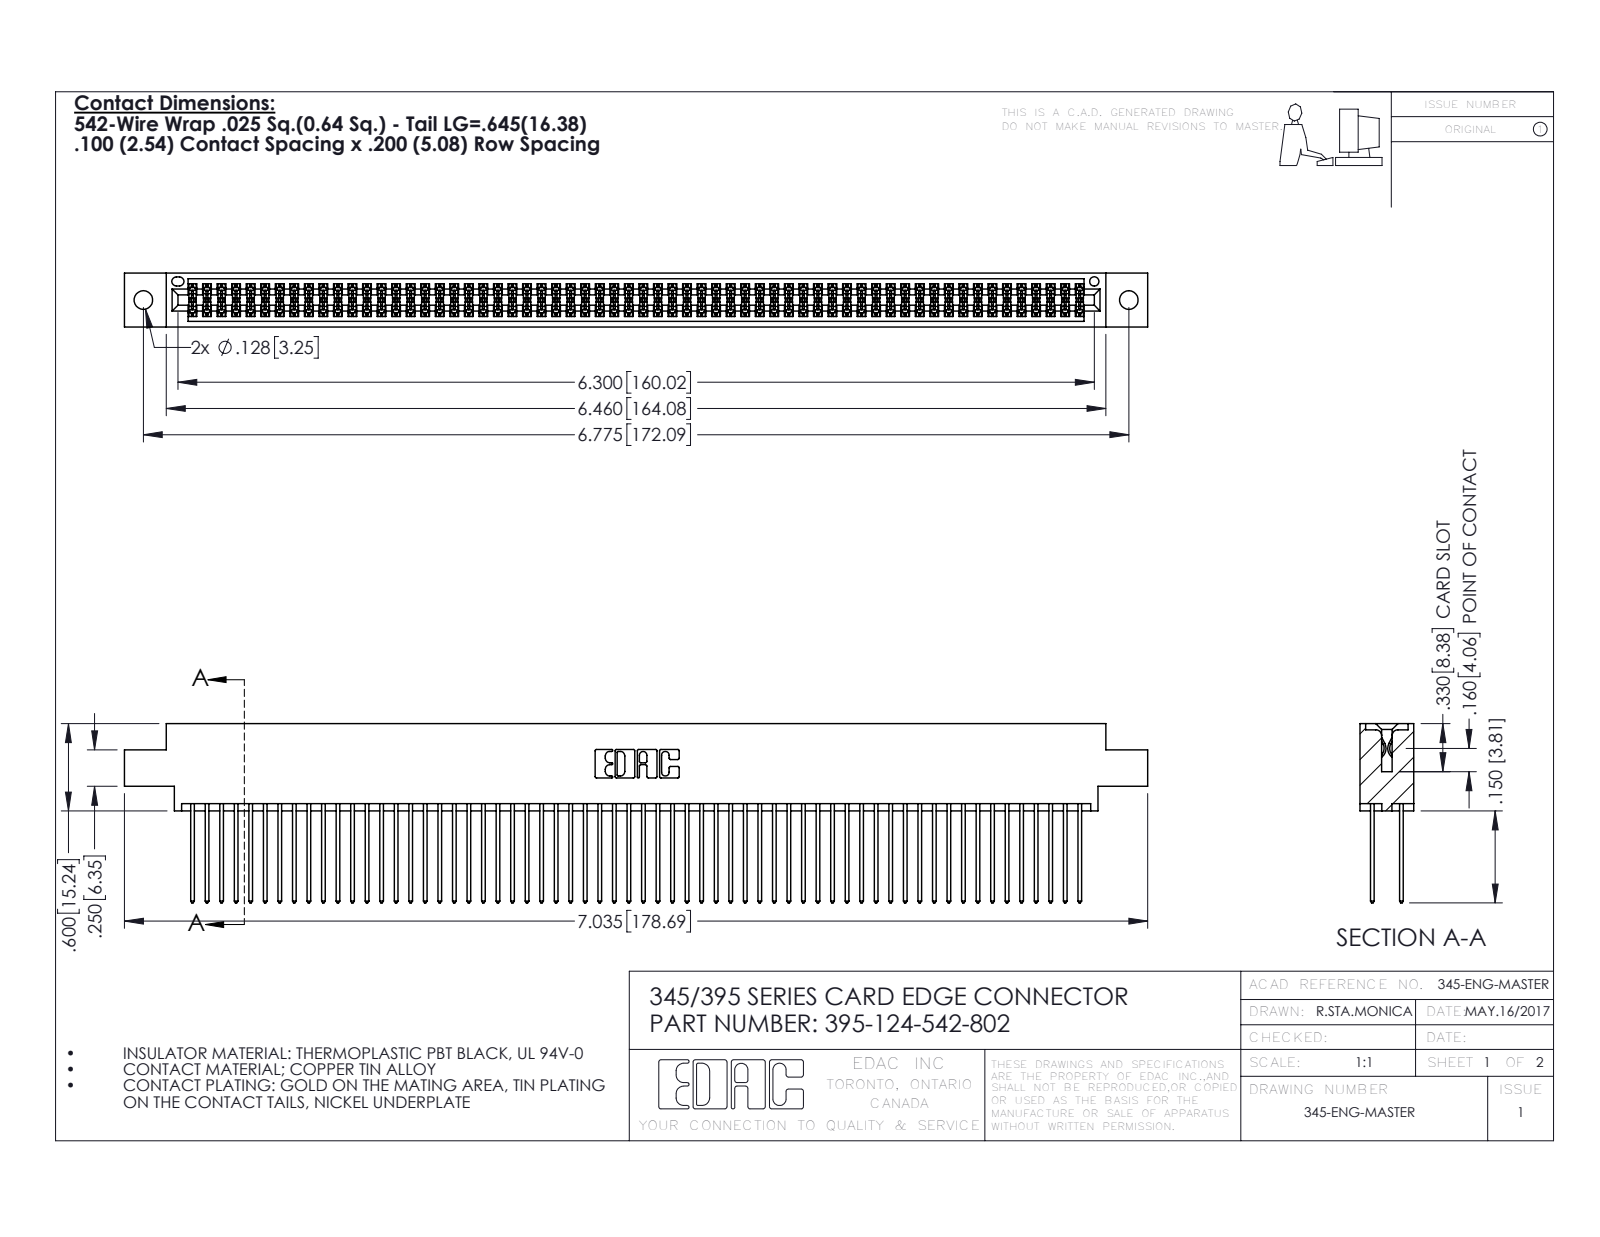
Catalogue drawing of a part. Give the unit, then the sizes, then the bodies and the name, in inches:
Units: inches
Overall size (bounding box): 7.035 × 1.232 × 0.37
Round holes (diameter × count): ⌀0.128 ×2, ⌀0.064 ×1
Partial cylindrical surfaces — rounded edges, fillets, slot ends (radius × count): R0.006 ×186, R0.01 ×124, R0.01 ×22, R0.007 ×6, R0.031 ×6, R0.026 ×3, R0.014 ×2, R0.019 ×2
Main face-to-face distances: 0.072, 0.298, 0.2, 0.098, 0.272, 0.025, 0.37, 0.225, 0.175, 0.149
Hole centre spacings: 0.27, 6.539, 6.775
Volume: 1.097 in³ · Surface area: 45.76 in²
Bodies: 125 solids, 6330 faces (4176 planar, 2154 cylindrical, 0 other)
Part name (STEP PRODUCT): 345-292-001_345-293-142; 395-124-542-802; 345 Part_0.170 Offset - 0.128 Dia
STEP written by: SolidWorks 2016 (CONFIG_CONTROL_DESIGN)
